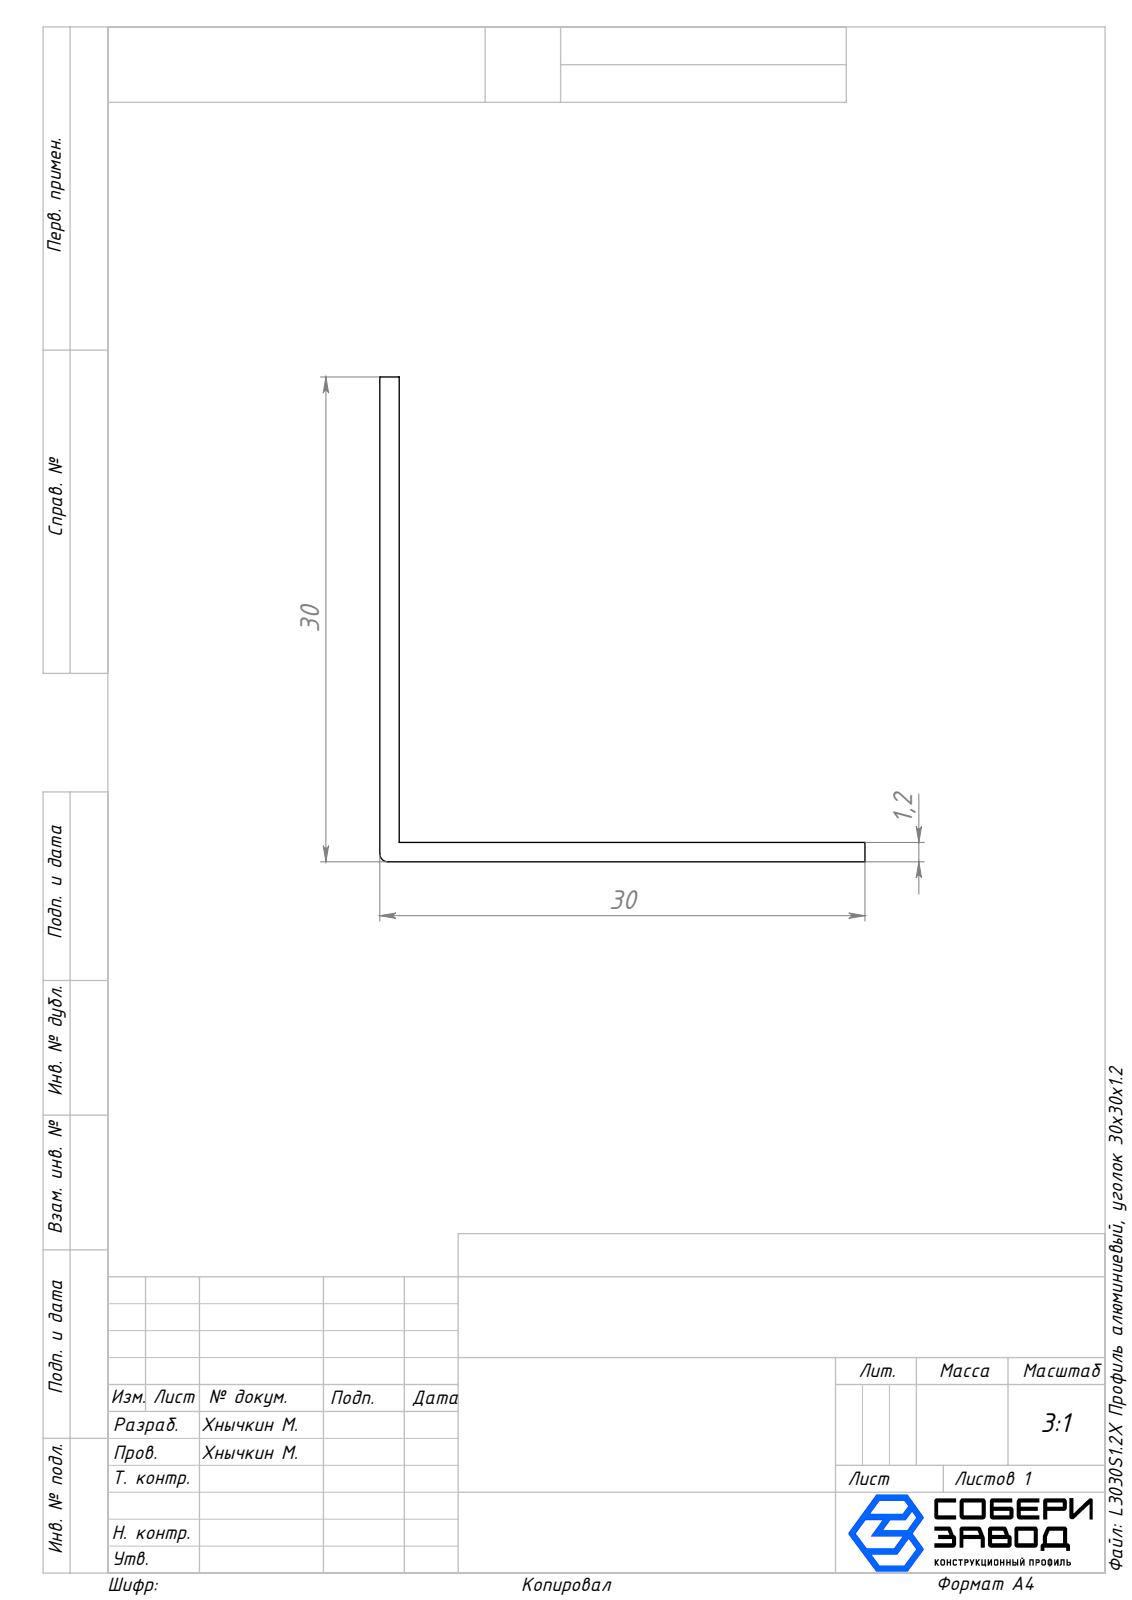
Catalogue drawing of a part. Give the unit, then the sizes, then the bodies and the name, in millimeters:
Units: millimetres
Overall size (bounding box): 1000 × 30 × 30
Partial cylindrical surfaces — rounded edges, fillets, slot ends (radius × count): R0.5 ×1
Main face-to-face distances: 1.2, 30, 28.8, 1000
Volume: 70 506 mm³ · Surface area: 119 926 mm²
Bodies: 1 solid, 9 faces (8 planar, 1 cylindrical, 0 other)
Part name (STEP PRODUCT): L3030S1.2X Профиль алюминиевый, уголок 30х30х1.2
STEP written by: SolidWorks 2025 (AUTOMOTIVE_DESIGN)
